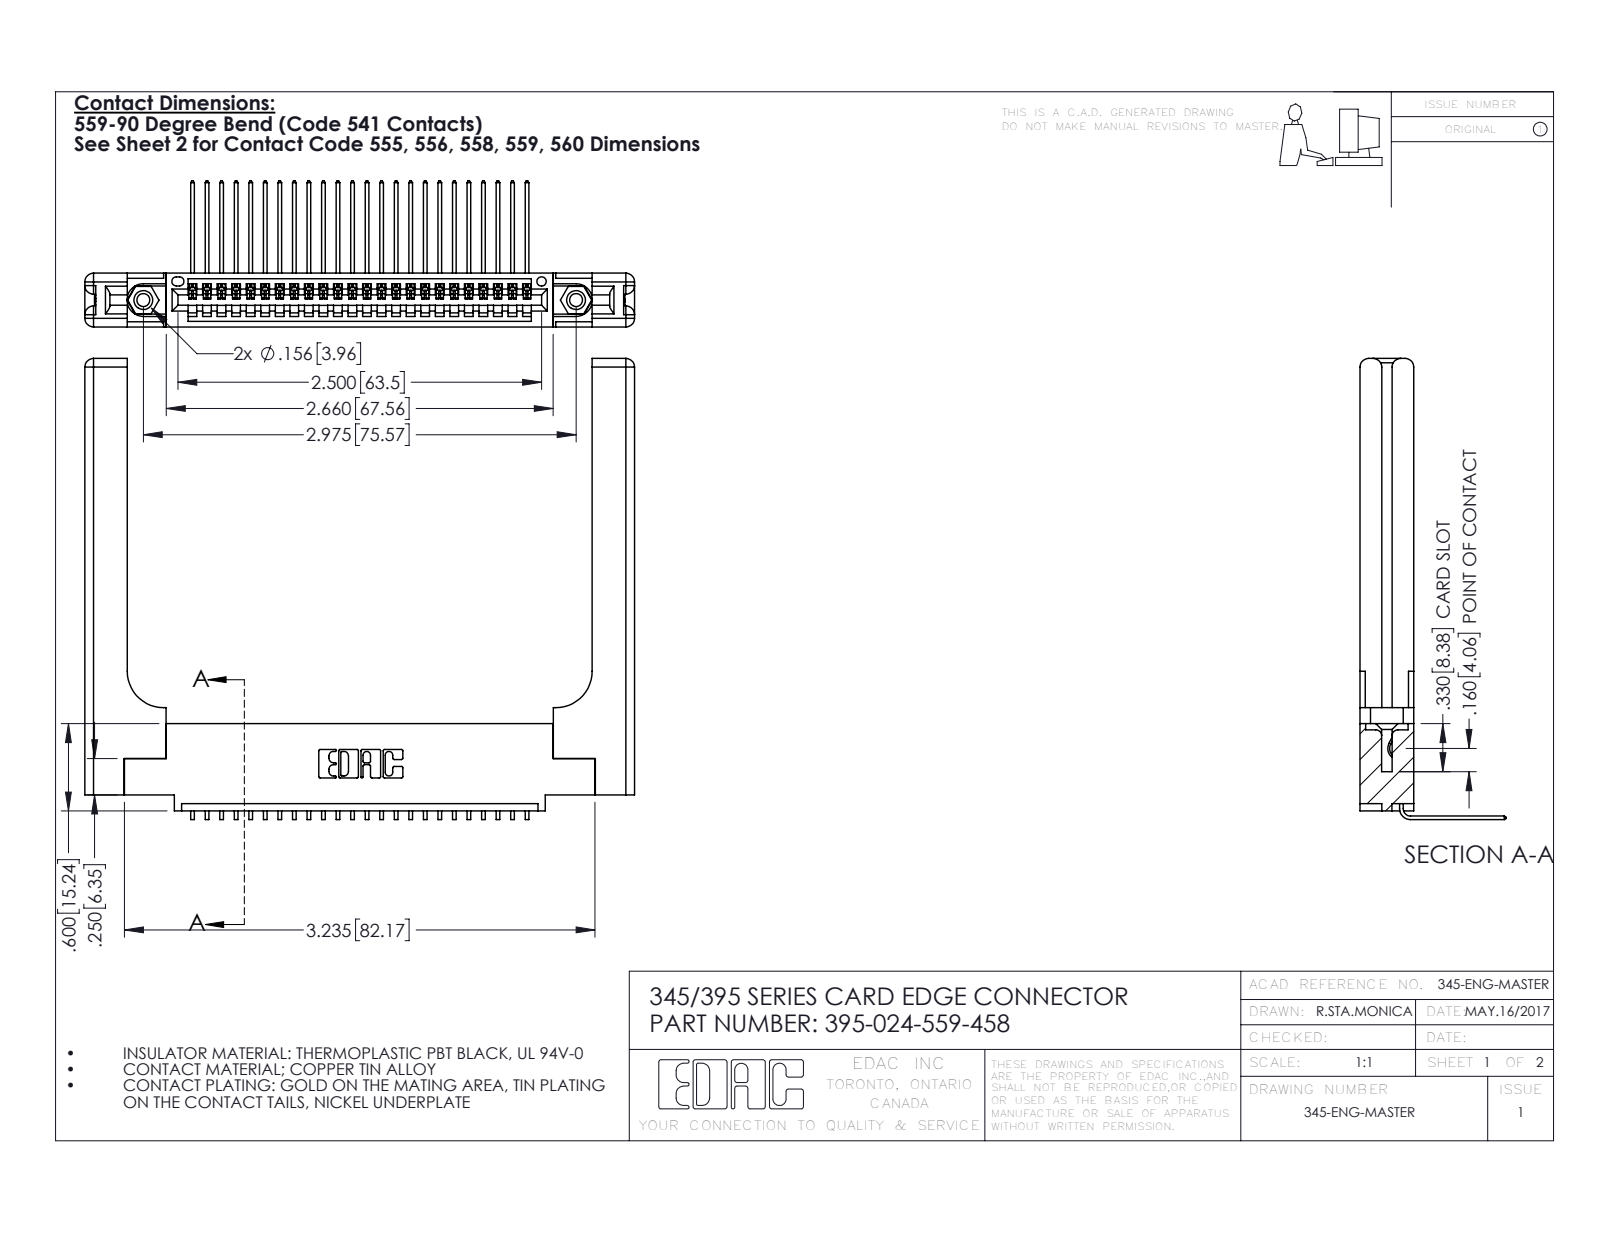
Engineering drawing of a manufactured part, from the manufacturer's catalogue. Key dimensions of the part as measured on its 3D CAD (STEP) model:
Part name (STEP PRODUCT): 345-250-001_345-250-001-102; 395-024-559-458; 345 Part_0.110 Offset - 0.156 Dia-TH; 345-292-001_558 559 Tail - 1 (+1 more)
STEP written by: SolidWorks 2016 (CONFIG_CONTROL_DESIGN)
Units: inches
Bodies: 29 solids, 1826 faces (1240 planar, 526 cylindrical, 60 other)
Overall size (bounding box): 3.779 × 3.169 × 1.005
Volume: 1.067 in³ · Surface area: 27.19 in²
Round holes (diameter × count): ⌀0.089 ×2, ⌀0.125 ×2, ⌀0.156 ×2, ⌀0.064 ×1
Round bosses / shafts (diameter × count): ⌀0.155 ×2
Partial cylindrical surfaces — rounded edges, fillets, slot ends (radius × count): R0.006 ×48, R0.01 ×22, R0.06 ×16, R0.007 ×6, R0.031 ×6, R0.026 ×3, R0.03 ×2, R0.031 ×2
Main face-to-face distances: 0.37, 0.072, 0.298, 0.148, 0.15, 0.077, 0.22, 0.098, 0.272, 0.025
Hole centre spacings: 0.27, 2.741, 2.975
